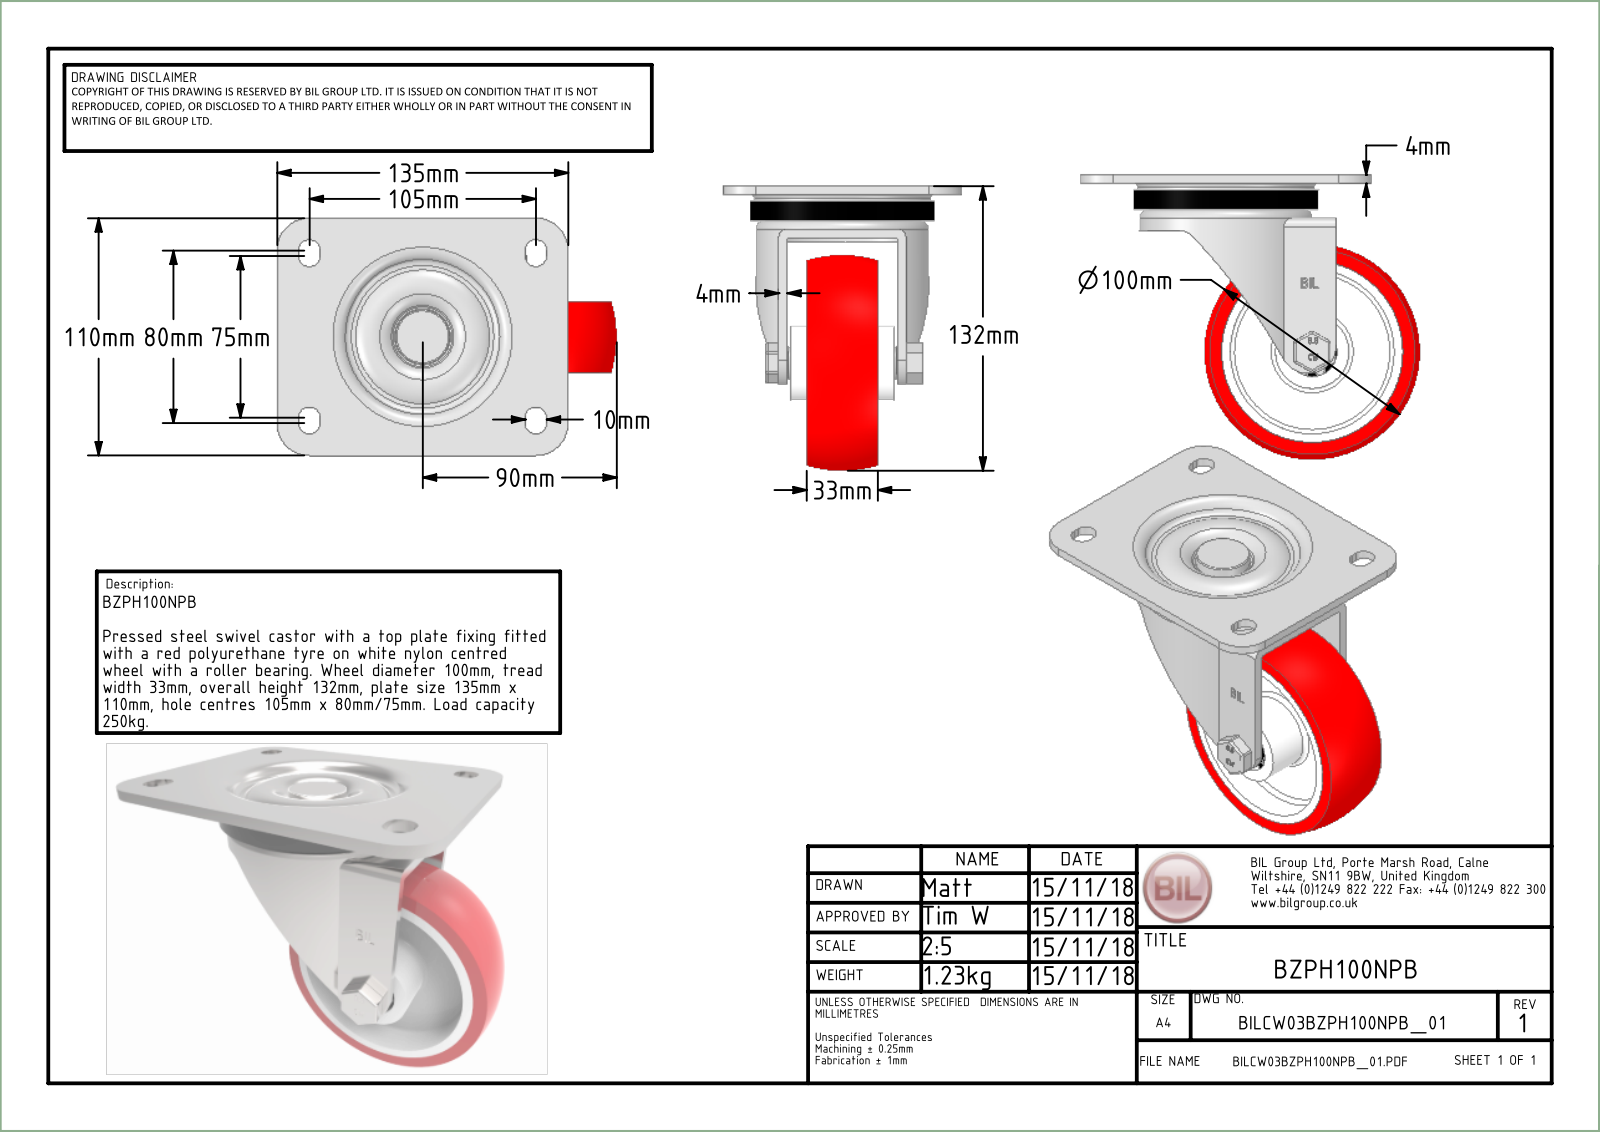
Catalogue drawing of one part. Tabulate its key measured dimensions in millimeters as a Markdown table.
| quantity | value |
| --- | --- |
| part name | BZPH100NPB v3; BZPH100AS v1; ZINC PLATED, PRESSED STEEL TOP PLATE; ZINC PLATED, PRESSED STEEL FORKS (+8 more) |
| STEP written by | Autodesk Translation Framework v14.10.0.0 (AUTOMOTIVE_DESIGN) |
| units | millimeters |
| bodies | 20 solids, 488 faces (253 planar, 147 cylindrical, 88 other) |
| overall size | 157.5 × 132 × 110 |
| volume | 322 110 mm³ |
| surface area | 150 228 mm² |
| round holes (diameter × count) | 10 × 1, 10.2 × 1, 10.5 × 1, 12 × 1, 15 × 1, 15.5 × 1, 23.5 × 1, 26 × 1, 27 × 1, 28 × 1, 72 × 1, 81 × 1 |
| round bosses / shafts (diameter × count) | 4 × 8, 83.5 × 1, 80 × 1, 51 × 1, 32 × 1, 30.5 × 1, 26.9 × 1, 25 × 1 |
| partial cylindrical surfaces (radius × count) | 0.5 × 18, 5.5 × 8, 0.75 × 6, 2 × 4, 15 × 4, 4 × 2, 10 × 1, 13.6 × 1 |
| main face-to-face distances | 4, 9, 13, 27.5, 19, 15, 23.5, 12.5, 31.5, 46.5 |
